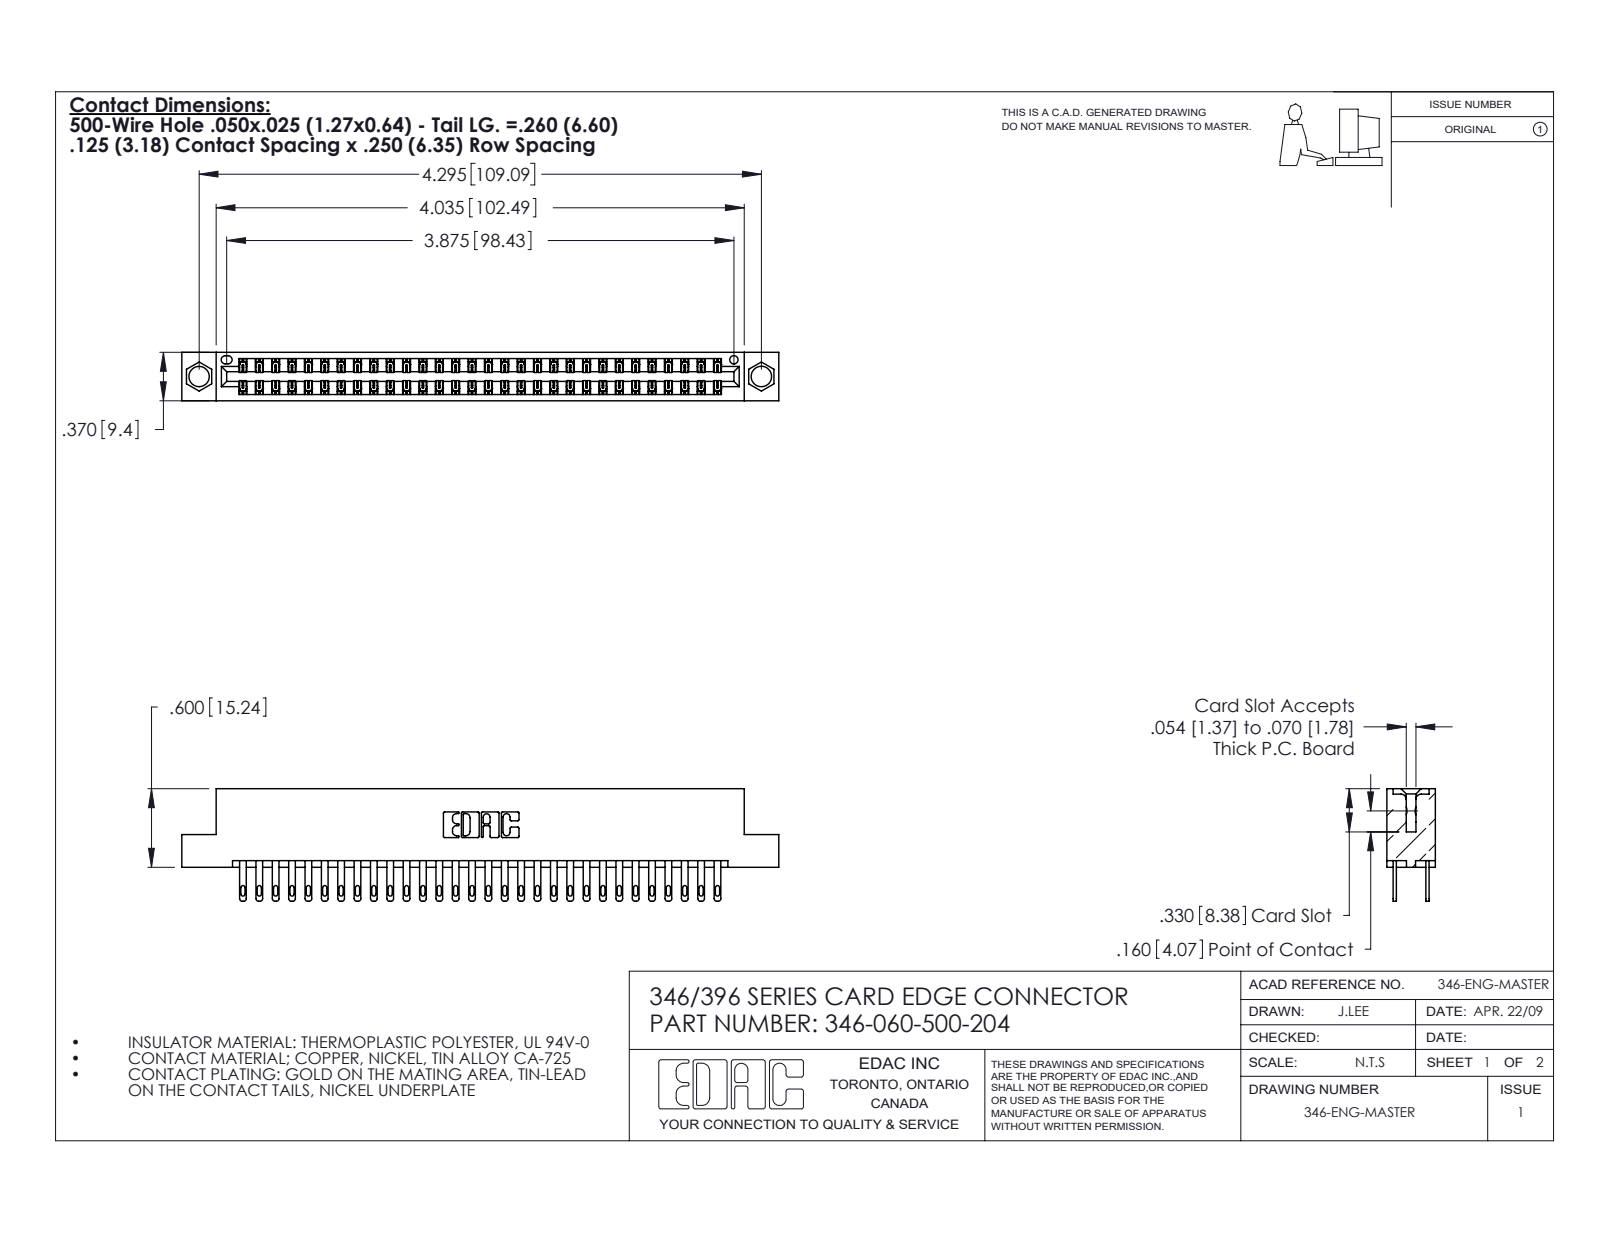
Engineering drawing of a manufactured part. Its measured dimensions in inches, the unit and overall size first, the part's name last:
Units: inches
Overall size (bounding box): 4.56 × 0.86 × 0.37
Round holes (diameter × count): ⌀0.156 ×2, ⌀0.064 ×1
Partial cylindrical surfaces — rounded edges, fillets, slot ends (radius × count): R0.006 ×90, R0.016 ×60, R0.02 ×60, R0.01 ×22, R0.007 ×6, R0.031 ×6, R0.026 ×3, R0.014 ×2
Main face-to-face distances: 0.048, 0.322, 0.25, 0.37, 0.072, 0.298, 0.025, 0.275, 0.148, 0.222
Hole centre spacings: 0.246, 4.087, 4.295
Volume: 0.688 in³ · Surface area: 24.48 in²
Bodies: 61 solids, 3016 faces (1830 planar, 1186 cylindrical, 0 other)
Part name (STEP PRODUCT): 345-292-001_345-293-100; 346 Part_Flush Mounting Lugs - 0.156 Dia-TH; 346-060-500-204
STEP written by: SolidWorks 2020 (CONFIG_CONTROL_DESIGN)
